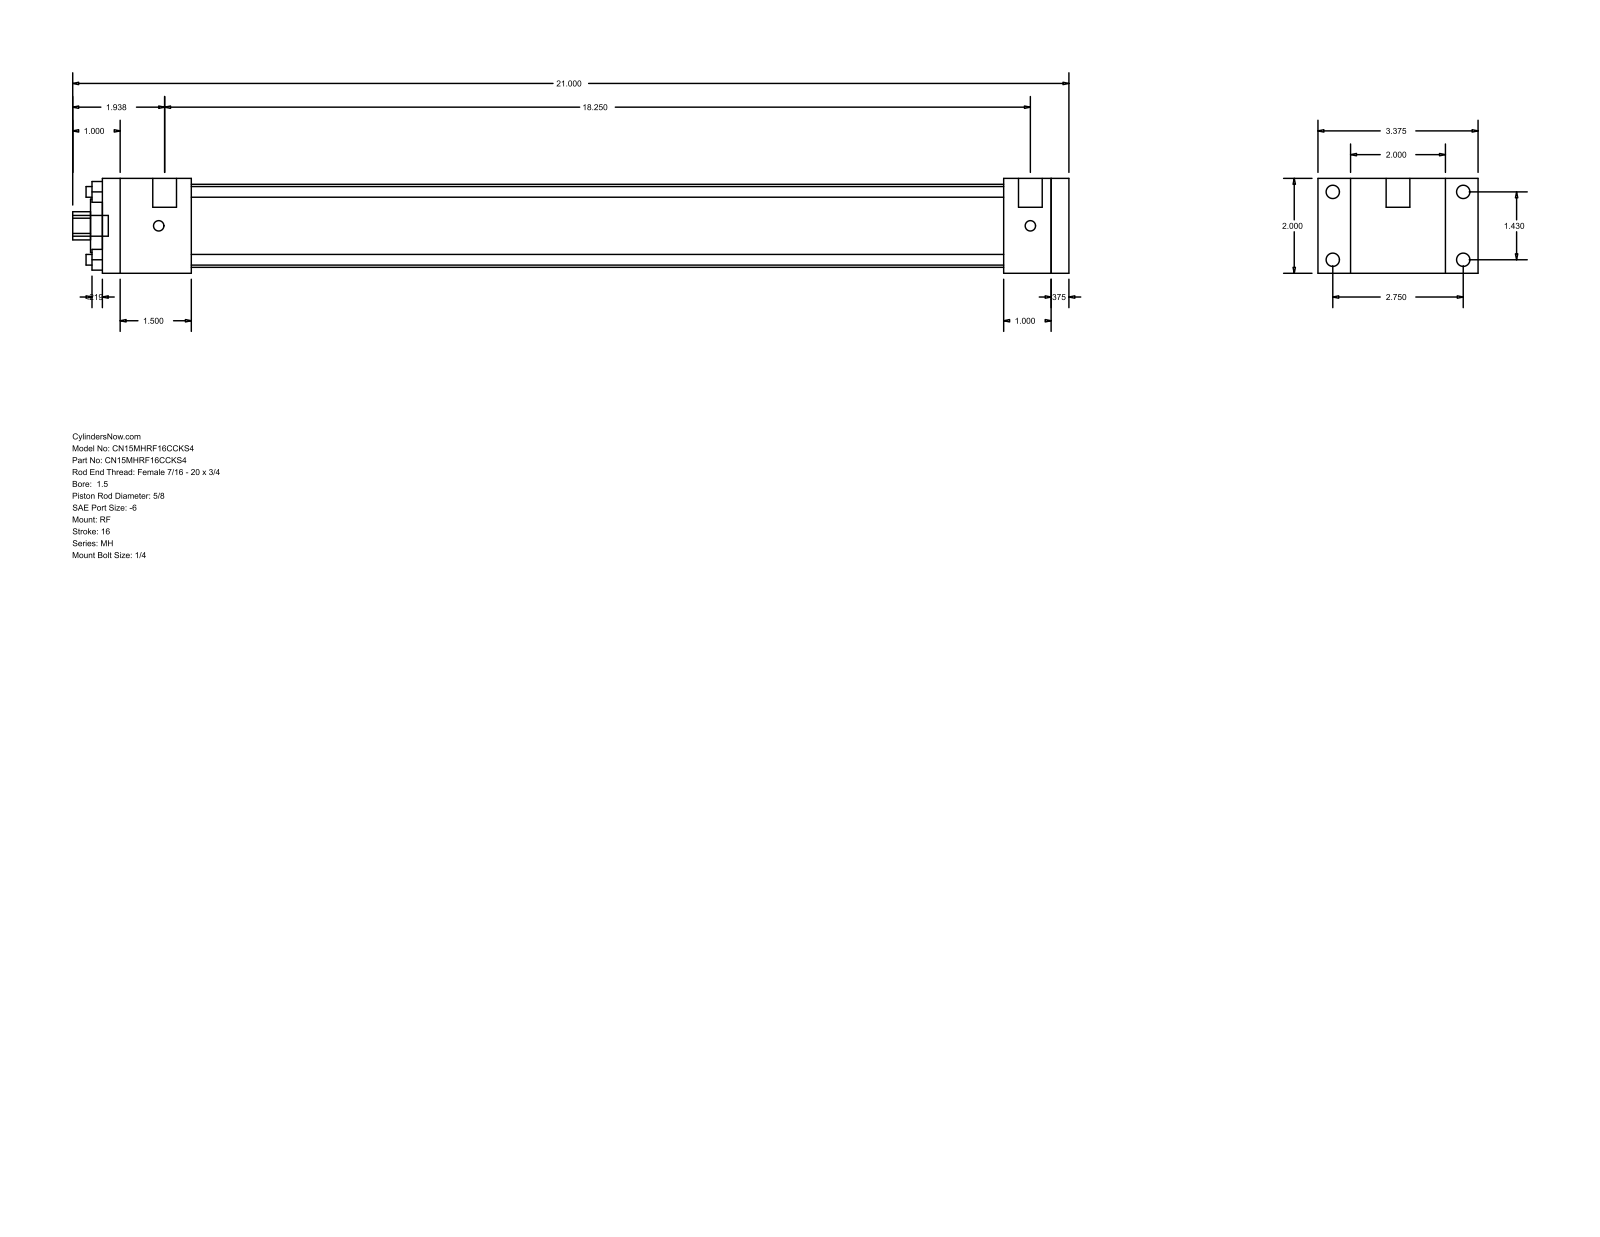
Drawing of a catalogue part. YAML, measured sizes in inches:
part_name: "MH_RF__0150_0.625"
step_written_by: "GSSL Pune (CONFIG_CONTROL_DESIGN)"
units: inches
bodies: {solids: 0, faces: 92, planar: 64, cylindrical: 28, other: 0}
overall_size: [21, 3.375, 2]
round_holes:
  - {diameter: 0.225, count: 4}
  - {diameter: 0.625, count: 1}
  - {diameter: 1.125, count: 1}
  - {diameter: 1.75, count: 1}
round_bosses_or_shafts:
  - {diameter: 0.281, count: 4}
  - {diameter: 0.219, count: 4}
  - {diameter: 0.5, count: 2}
  - {diameter: 0.437, count: 1}
partial_cylinders:
  - {radius: 0.297, count: 1}
face_to_face_distances: [2, 0.375, 20, 20.375, 0.687, 2.687, 19, 1, 1.375, 1.875]
hole_center_spacings: [1.011, 1.43, 2.022]
